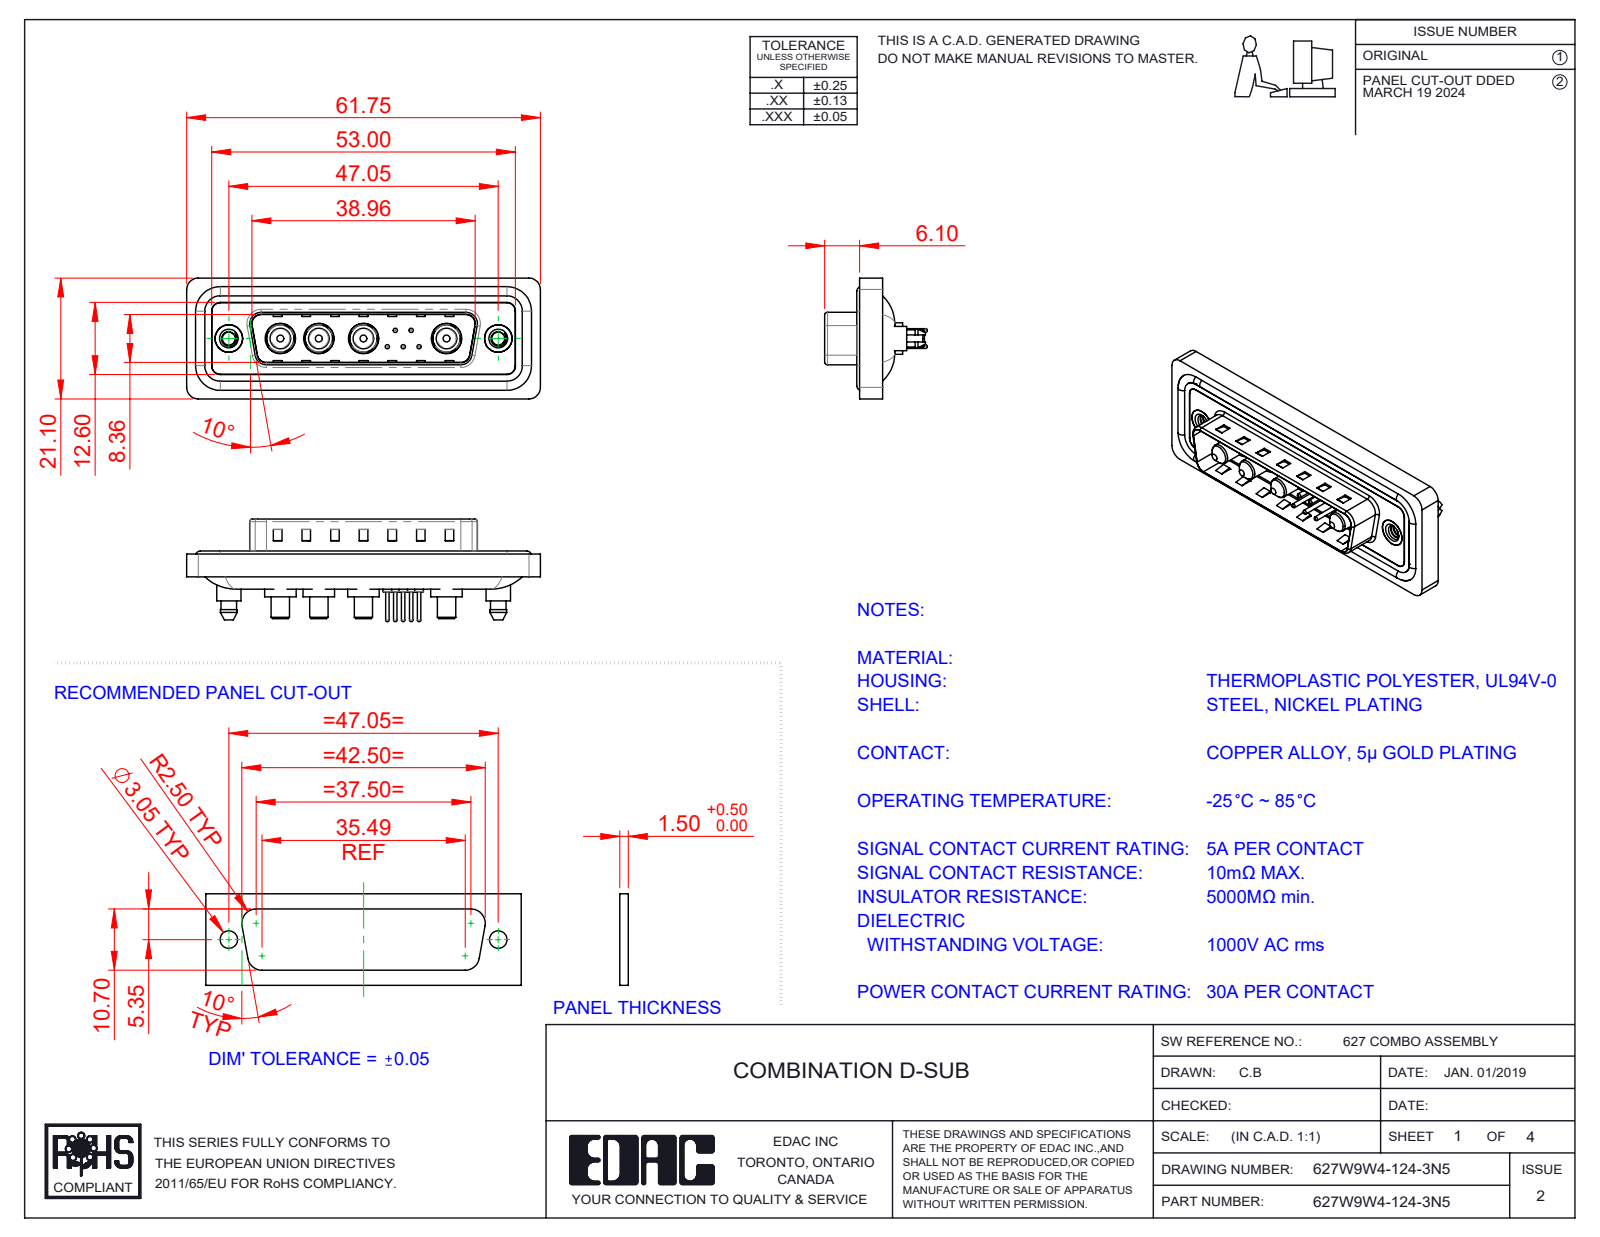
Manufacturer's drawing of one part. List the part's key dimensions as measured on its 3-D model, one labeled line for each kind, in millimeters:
Part name (STEP PRODUCT): 627Combo Contact Row 1_24; Power Pin_30A S; 627W9W4-124-3N5; 627Combo Housing_9W4 (+5 more)
STEP written by: SolidWorks 2023 (CONFIG_CONTROL_DESIGN)
Units: millimetres
Bodies: 20 solids, 874 faces (300 planar, 366 cylindrical, 208 other)
Overall size (bounding box): 61.75 × 21.1 × 17.9
Volume: 7 566 mm³ · Surface area: 12 187 mm²
Round holes (diameter × count): ⌀0.75 ×5, ⌀1.6 ×5, ⌀2 ×5, ⌀4.85 ×4, ⌀5.3 ×4, ⌀2.26 ×2, ⌀4 ×2, ⌀4.8 ×2, ⌀5 ×2
Round bosses / shafts (diameter × count): ⌀1.5 ×5, ⌀0.6 ×5, ⌀5.5 ×4, ⌀5.2 ×4, ⌀4.75 ×4, ⌀3.75 ×4, ⌀3.6 ×4, ⌀3.2 ×4
Partial cylindrical surfaces — rounded edges, fillets, slot ends (radius × count): R1.5 ×24, R2 ×18, R1.6 ×10, R0.5 ×8, R0.25 ×4, R0.6 ×4, R0.65 ×4, R0.9 ×4
Main face-to-face distances: 0.4, 1.5, 1.1, 0.5, 3.1, 1.6, 2.9, 0.82, 9.58, 5.65
Hole centre spacings: 3.16, 2.77, 5.04, 14.51, 2.78, 4.4, 4.41, 5
